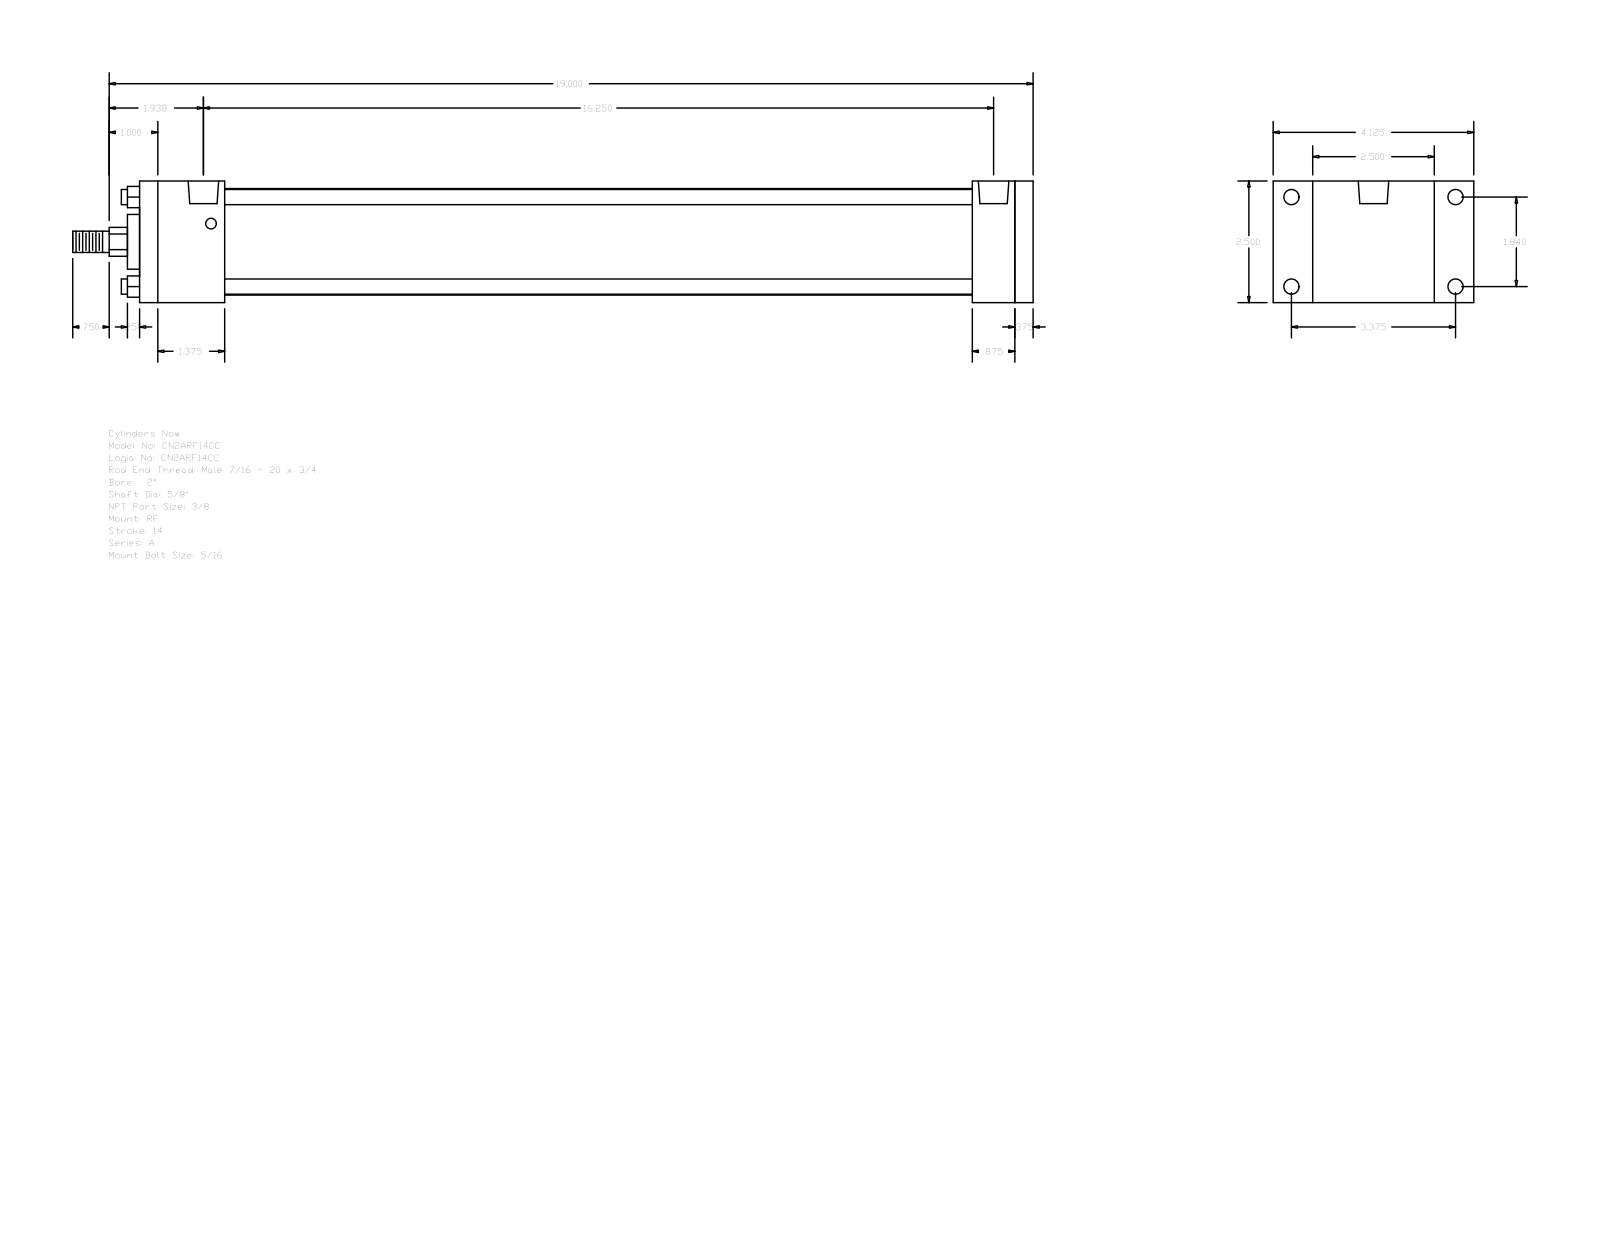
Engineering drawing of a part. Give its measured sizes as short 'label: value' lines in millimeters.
name: A_RF__0200_0.625
written by: GSSL Pune (CONFIG_CONTROL_DESIGN)
unit: mm
bodies: 0 solids, 92 faces (64 planar, 28 cylindrical, 0 other)
size: 501.65 × 104.78 × 63.5
holes: 4× ⌀5.56, 4× ⌀7.94, 2× ⌀15.93
bosses: 4× ⌀7.94, 1× ⌀55.63, 1× ⌀28.57, 1× ⌀15.88, 1× ⌀11.11
rounds: 1× R7.54
face distances: 63.5, 466.72, 9.53, 457.19, 44.45, 412.74, 422.27, 434.97, 390.52, 22.22
hole spacings: 46.74, 85.72, 97.63, 404.8, 3.97, 3.98, 408.77, 408.78
